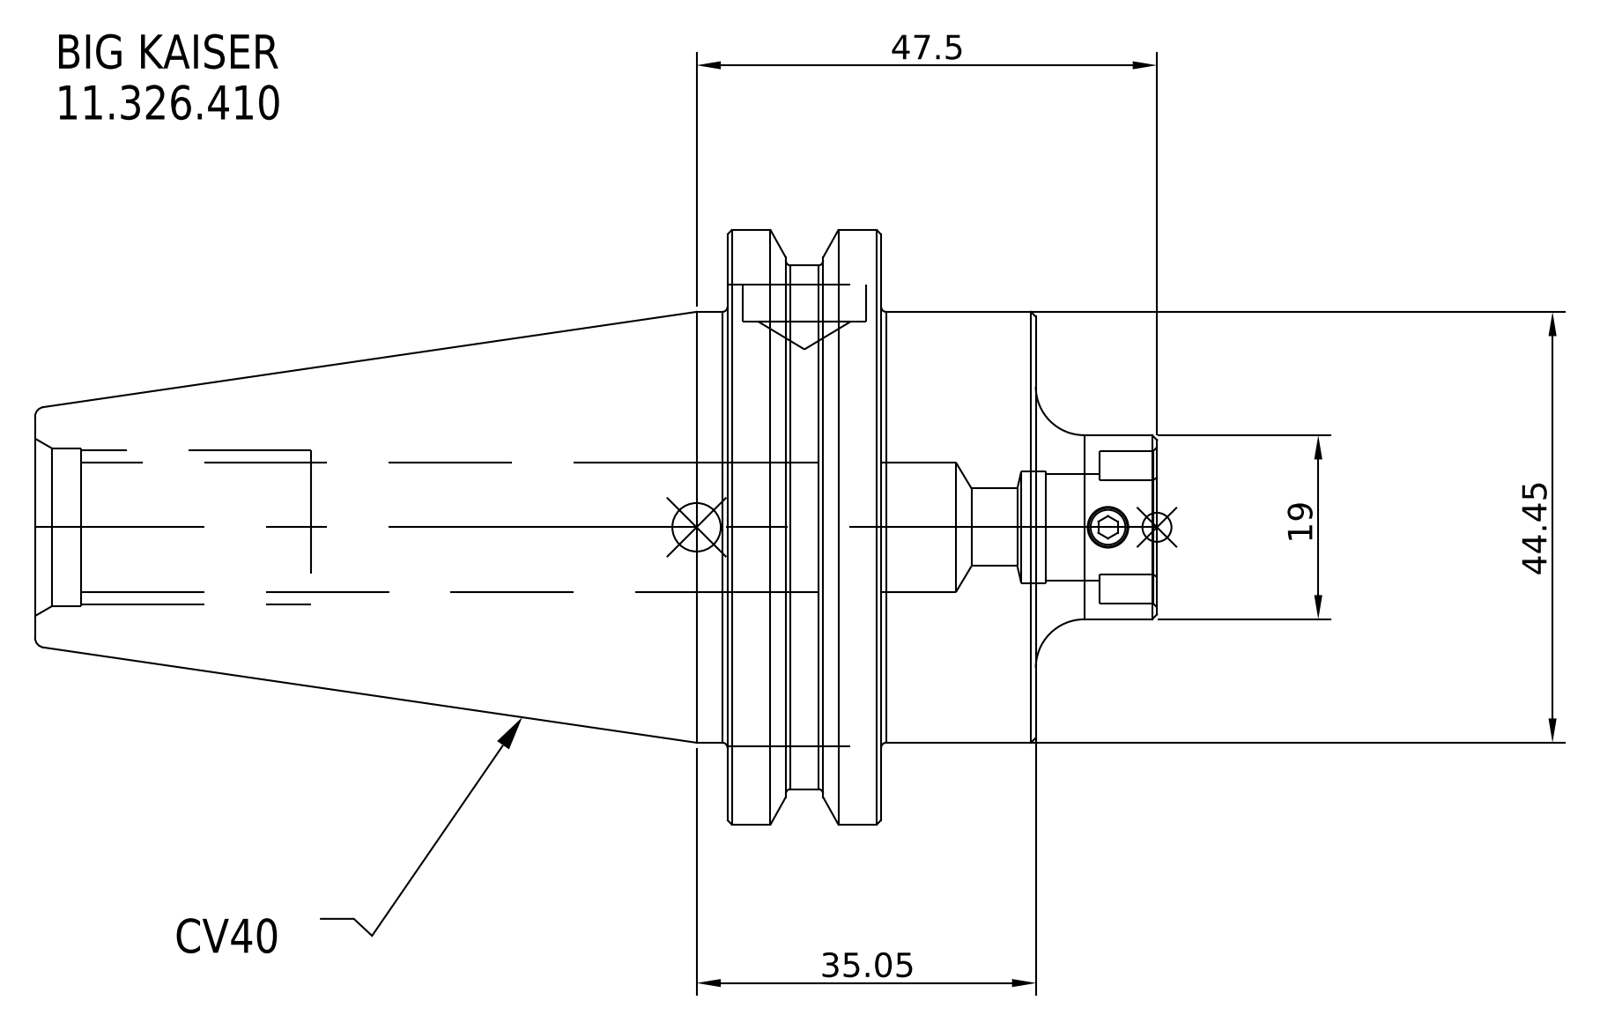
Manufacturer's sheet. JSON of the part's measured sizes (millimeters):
{"part_name": "11_326_410", "step_written_by": "SolidWorks 2021 (CONFIG_CONTROL_DESIGN)", "units": "millimeters", "bodies": {"solids": 1, "faces": 27, "planar": 7, "cylindrical": 12, "other": 8}, "overall_size": [115.75, 63.5, 63.5], "volume_mm3": 146032, "surface_area_mm2": 19984, "round_bosses_or_shafts": [[63.5, 1], [56.36, 1], [44.45, 1], [19, 1]], "face_to_face_distances": [15.88, 16, 31.88, 103.3, 87.3, 71.42, 12.45, 28.45, 44.33, 115.75]}
